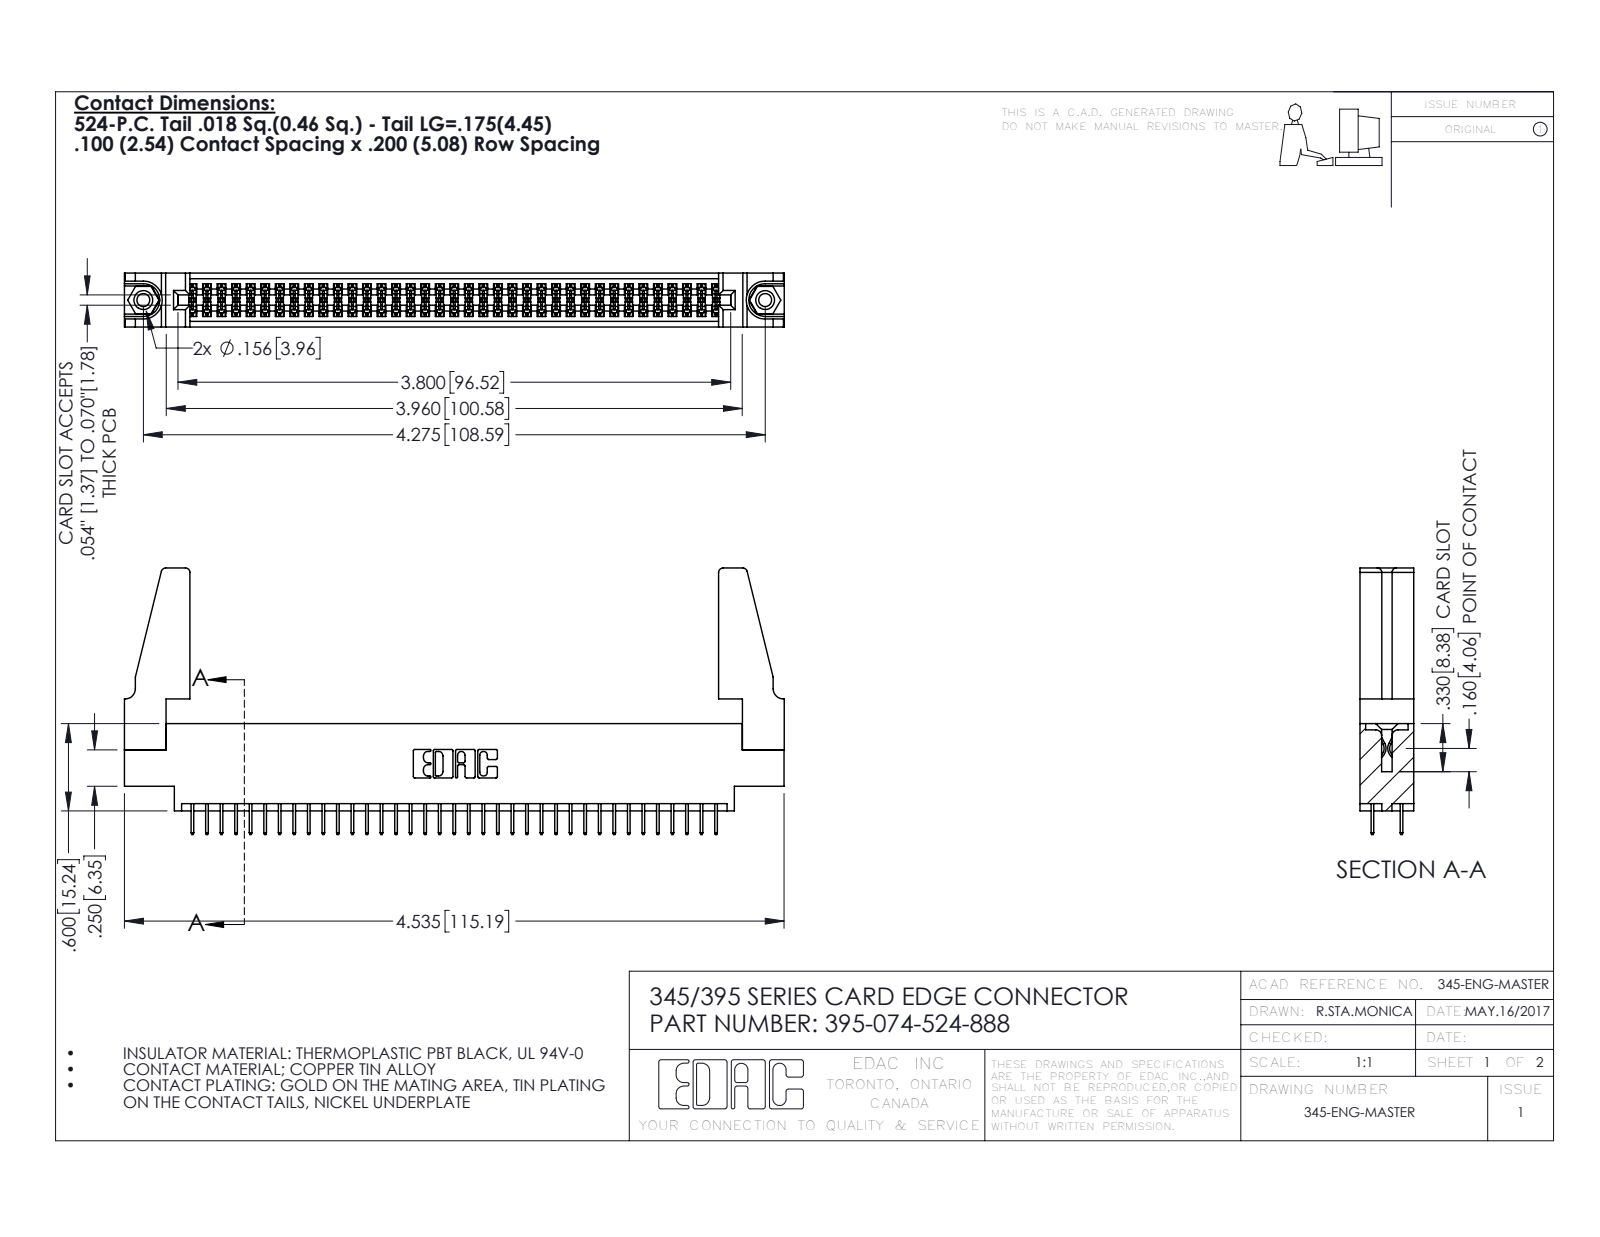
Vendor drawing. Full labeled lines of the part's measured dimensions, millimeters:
Part name (STEP PRODUCT): 345-250-001_345-250-001-102; 345-292-001_345-293-124; 345 Part_0.170 Offset - 0.156 Dia-TH; 345-220-078_345-220-088 (+1 more)
STEP written by: SolidWorks 2016 (CONFIG_CONTROL_DESIGN)
Units: millimetres
Bodies: 79 solids, 4250 faces (3042 planar, 1192 cylindrical, 16 other)
Overall size (bounding box): 115.2 × 46.5 × 9.4
Volume: 14 200 mm³ · Surface area: 19 010 mm²
Round holes (diameter × count): ⌀2.3 ×2, ⌀3.2 ×2, ⌀4 ×2, ⌀1.6 ×1
Round bosses / shafts (diameter × count): ⌀3.9 ×2
Partial cylindrical surfaces — rounded edges, fillets, slot ends (radius × count): R0.2 ×111, R0.3 ×22, R0.8 ×8, R0.2 ×6, R0.8 ×6, R0.7 ×3, R0.4 ×2, R0.5 ×2
Main face-to-face distances: 9.4, 1.8, 7.6, 5.1, 2.5, 6.9, 0.6, 5.7, 4.4, 1.8
Hole centre spacings: 6.9, 102.6, 108.6
